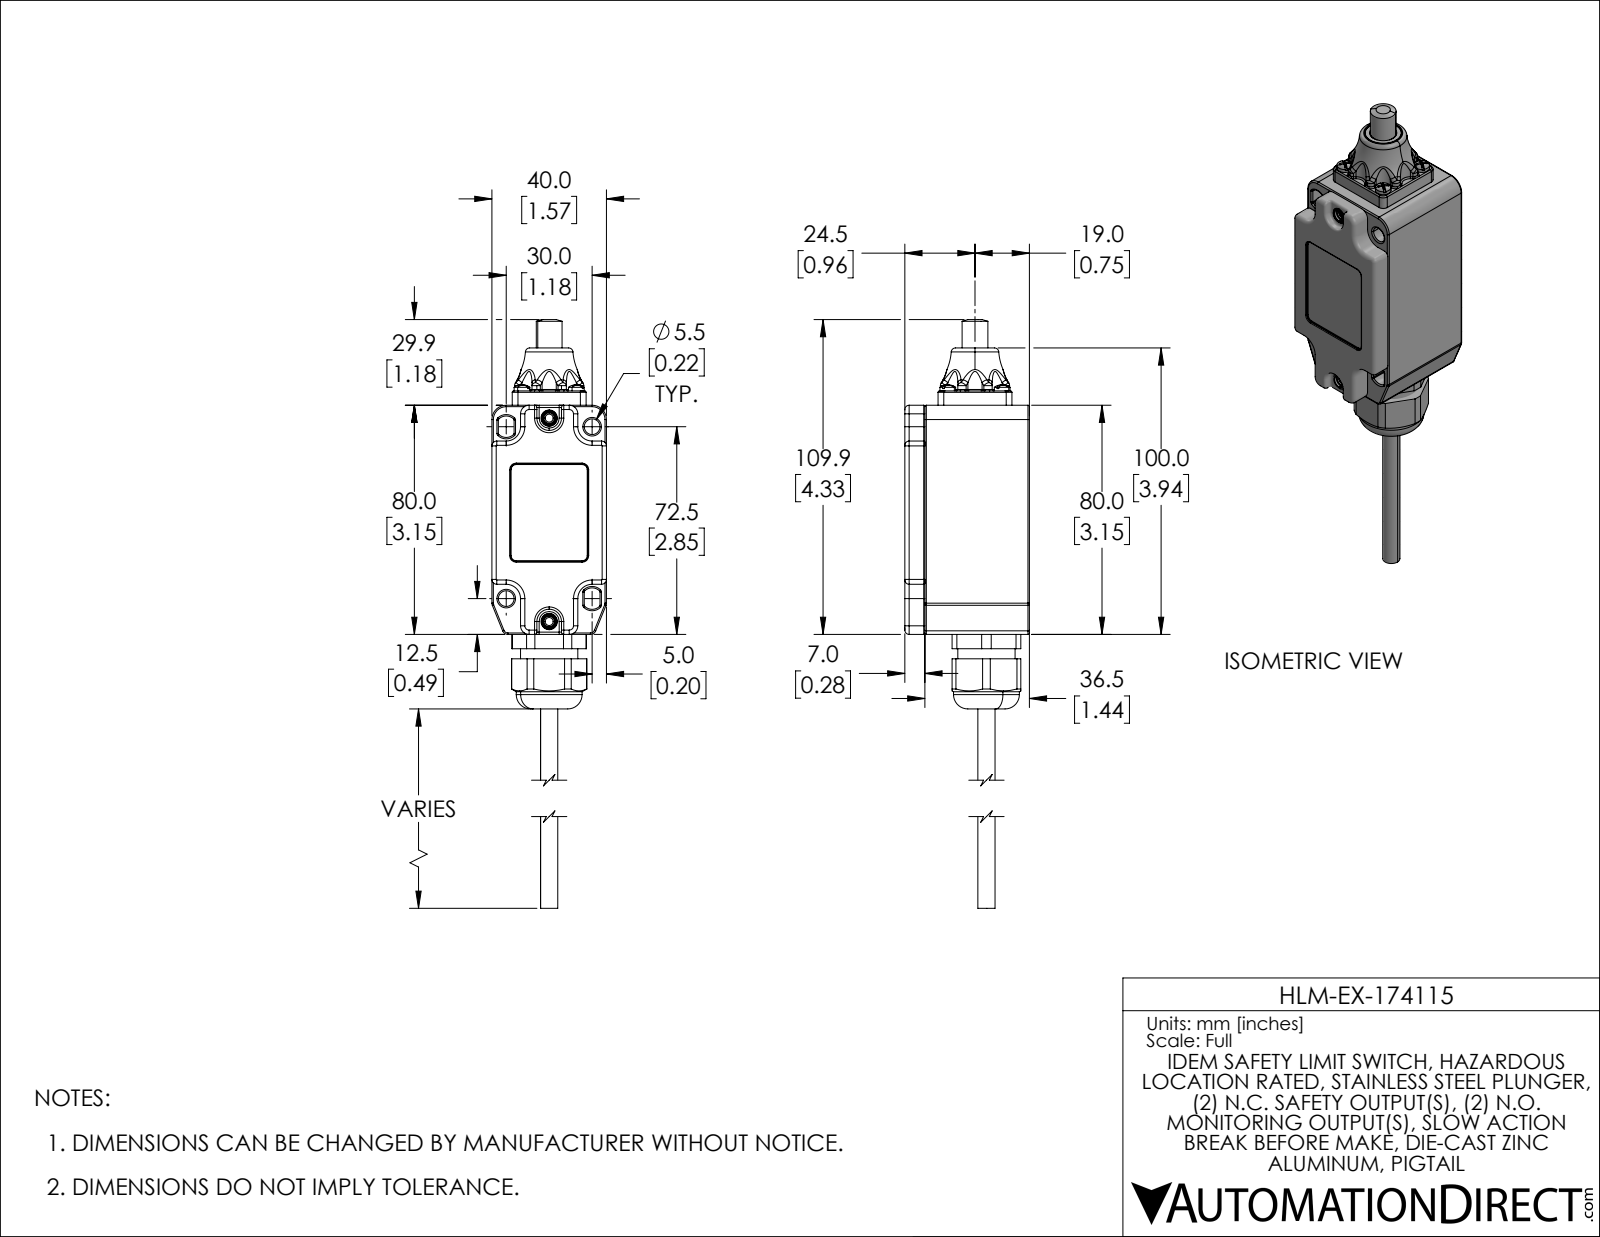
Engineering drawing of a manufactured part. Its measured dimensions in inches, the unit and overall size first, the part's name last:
Units: inches
Overall size (bounding box): 7.634 × 1.713 × 1.575
Round holes (diameter × count): ⌀0.118 ×10, ⌀0.13 ×4, ⌀0.146 ×2, ⌀0.15 ×2, ⌀0.157 ×2, ⌀0.165 ×2, ⌀0.217 ×2, ⌀0.354 ×2, ⌀0.138 ×1, ⌀0.173 ×1, ⌀0.22 ×1, ⌀0.272 ×1
Round bosses / shafts (diameter × count): ⌀0.244 ×6, ⌀0.216 ×4, ⌀0.252 ×2, ⌀0.906 ×1, ⌀0.728 ×1, ⌀0.551 ×1, ⌀0.504 ×1, ⌀0.453 ×1
Partial cylindrical surfaces — rounded edges, fillets, slot ends (radius × count): R0.02 ×169, R0.016 ×26, R0.006 ×14, R0.067 ×12, R0.079 ×12, R0.031 ×10, R0.039 ×9, R0.059 ×9
Main face-to-face distances: 0.089, 1.486, 1.575, 0.098, 1.398, 1.512, 0.276, 1.61, 0.102, 0.173
Hole centre spacings: 0.748, 0.529, 0.354, 0.432, 0.65, 0.75, 0.828, 0.854
Volume: 4.43 in³ · Surface area: 76.86 in²
Bodies: 12 solids, 1935 faces (460 planar, 539 cylindrical, 936 other)
Part name (STEP PRODUCT): HLM-EX-174115
STEP written by: SolidWorks 2021 (AUTOMOTIVE_DESIGN)
